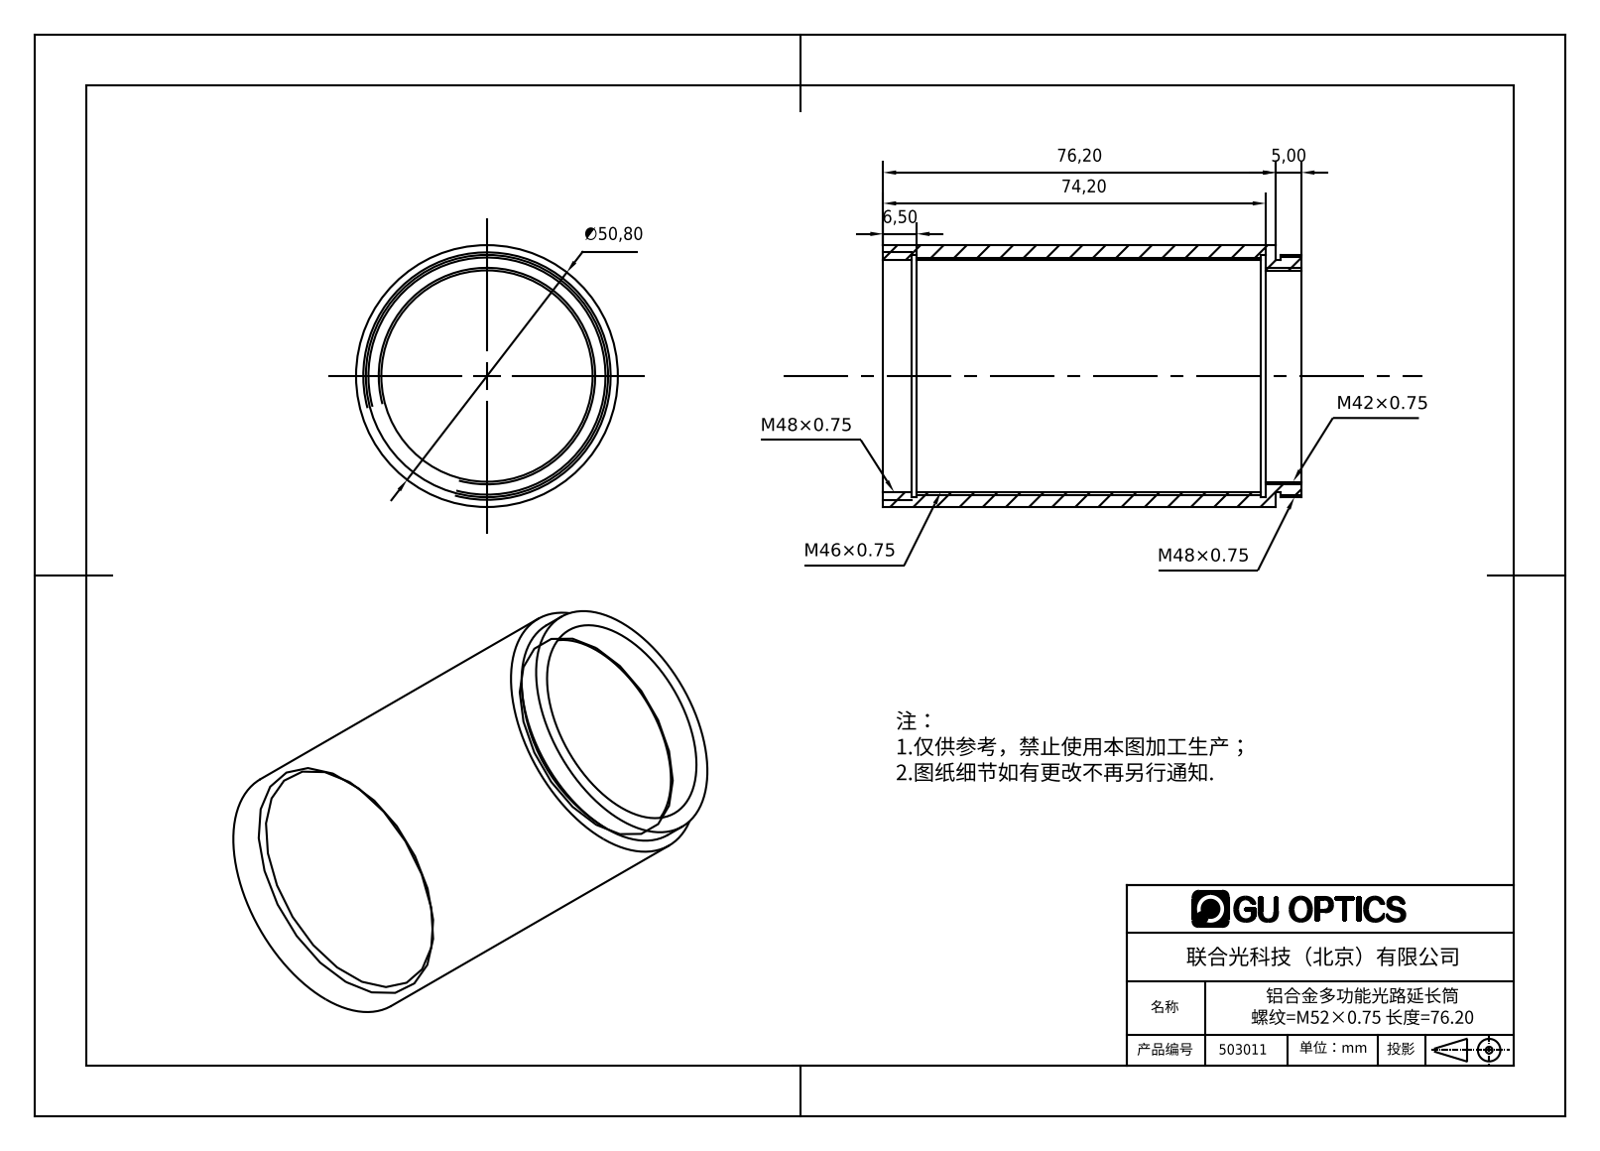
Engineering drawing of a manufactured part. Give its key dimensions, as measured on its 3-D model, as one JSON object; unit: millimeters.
{"part_name": "503011", "step_written_by": "SolidWorks 2016 (AUTOMOTIVE_DESIGN)", "units": "millimeters", "bodies": {"solids": 1, "faces": 24, "planar": 8, "cylindrical": 16, "other": 0}, "overall_size": [81.2, 50.8, 50.8], "volume_mm3": 35434, "surface_area_mm2": 26577, "round_holes": [[41, 1], [45, 1], [47, 1]], "round_bosses_or_shafts": [[50.8, 1]], "face_to_face_distances": [76.2, 1, 81.2, 5, 74.2, 2, 7, 3, 4, 67.7]}
